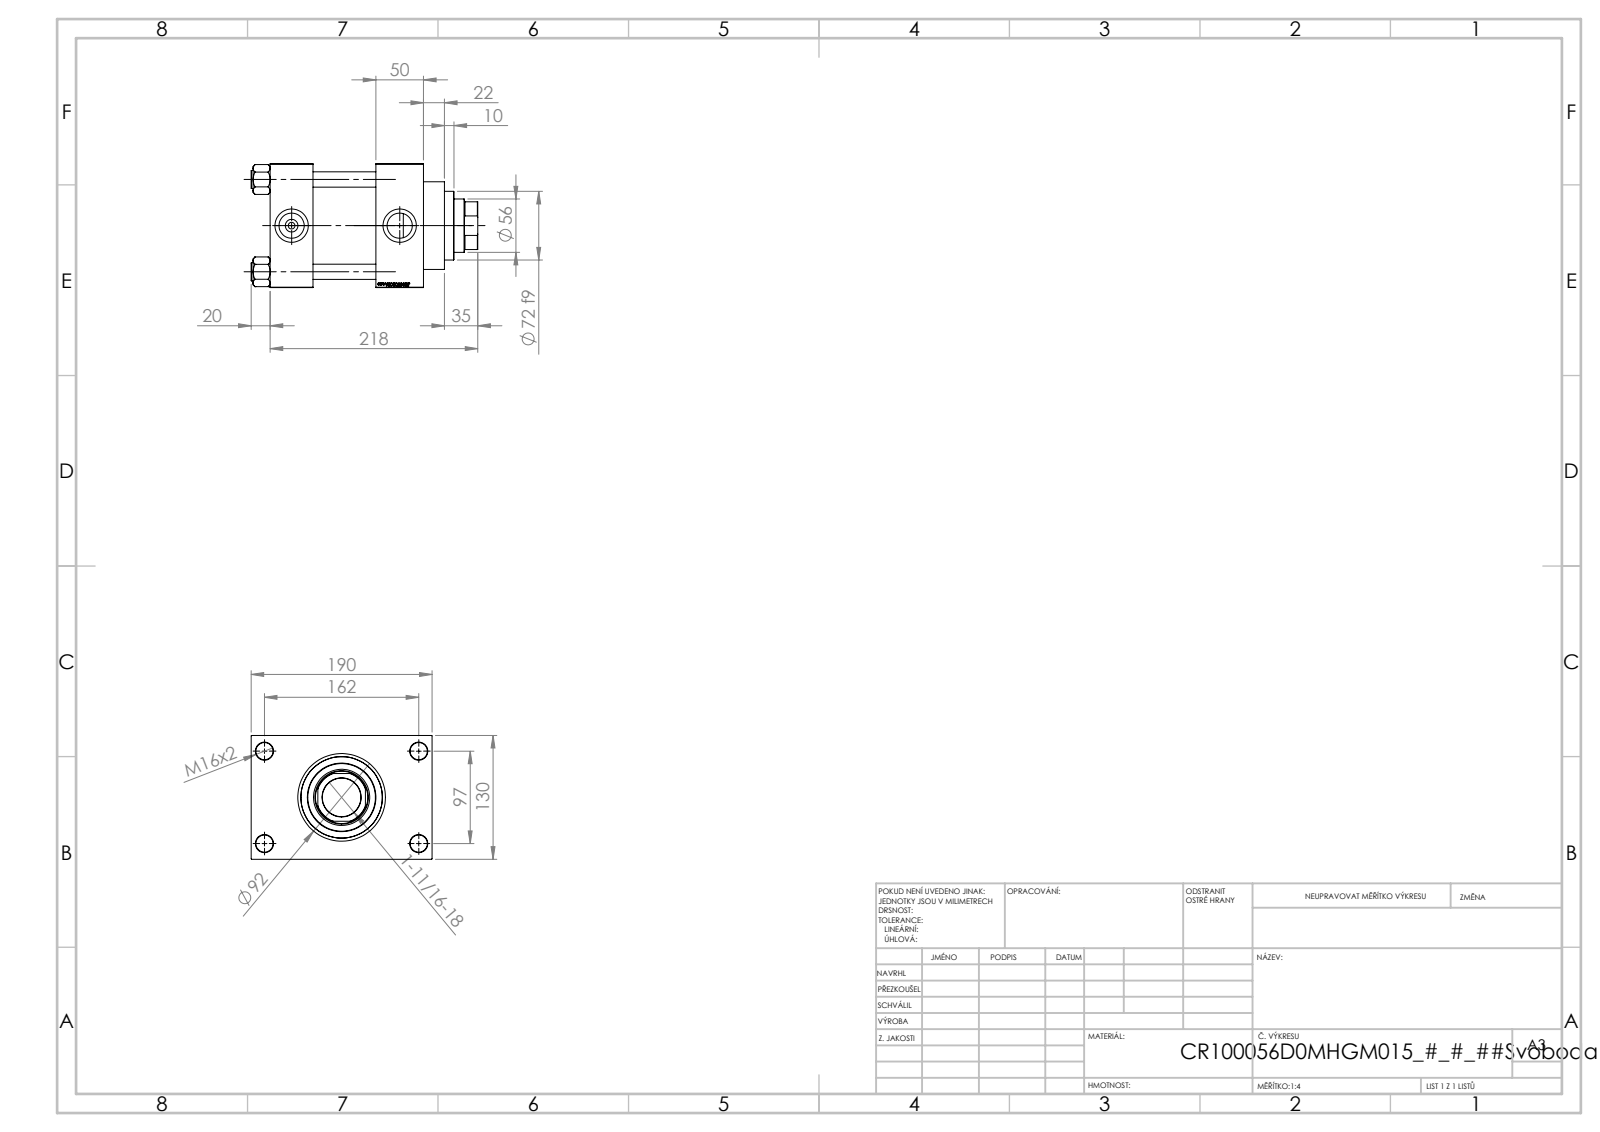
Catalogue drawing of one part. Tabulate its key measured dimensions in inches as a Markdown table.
| quantity | value |
| --- | --- |
| part name | V215CR_VCP_D; NUT_M5_D; V215CR_D_Body; V215CR_D_TYCINKA (+1 more) |
| STEP written by | SolidWorks 2019 (CONFIG_CONTROL_DESIGN) |
| units | inches |
| bodies | 11 solids, 1151 faces (545 planar, 88 cylindrical, 518 other) |
| overall size | 9.37 × 7.48 × 5.118 |
| volume | 159.1 in³ |
| surface area | 553.7 in² |
| round holes (diameter × count) | 0.63 × 4, 0.709 × 4, 0.276 × 2, 1.041 × 2, 1.378 × 2, 1.594 × 1, 2.205 × 1, 2.323 × 1, 2.992 × 1, 3.366 × 1, 3.937 × 1 |
| round bosses / shafts (diameter × count) | 0.748 × 4, 4.173 × 1, 3.622 × 1, 2.835 × 1 |
| partial cylindrical surfaces (radius × count) | 1.063 × 1 |
| main face-to-face distances | 5.118, 4.567, 1.969, 1.772, 4.37, 2.598, 6.339, 1.181, 6.299, 2.559 |
| hole center spacings | 1.281, 2.698, 3.717, 3.815, 4.026, 5.096, 6.367, 3.819 |
